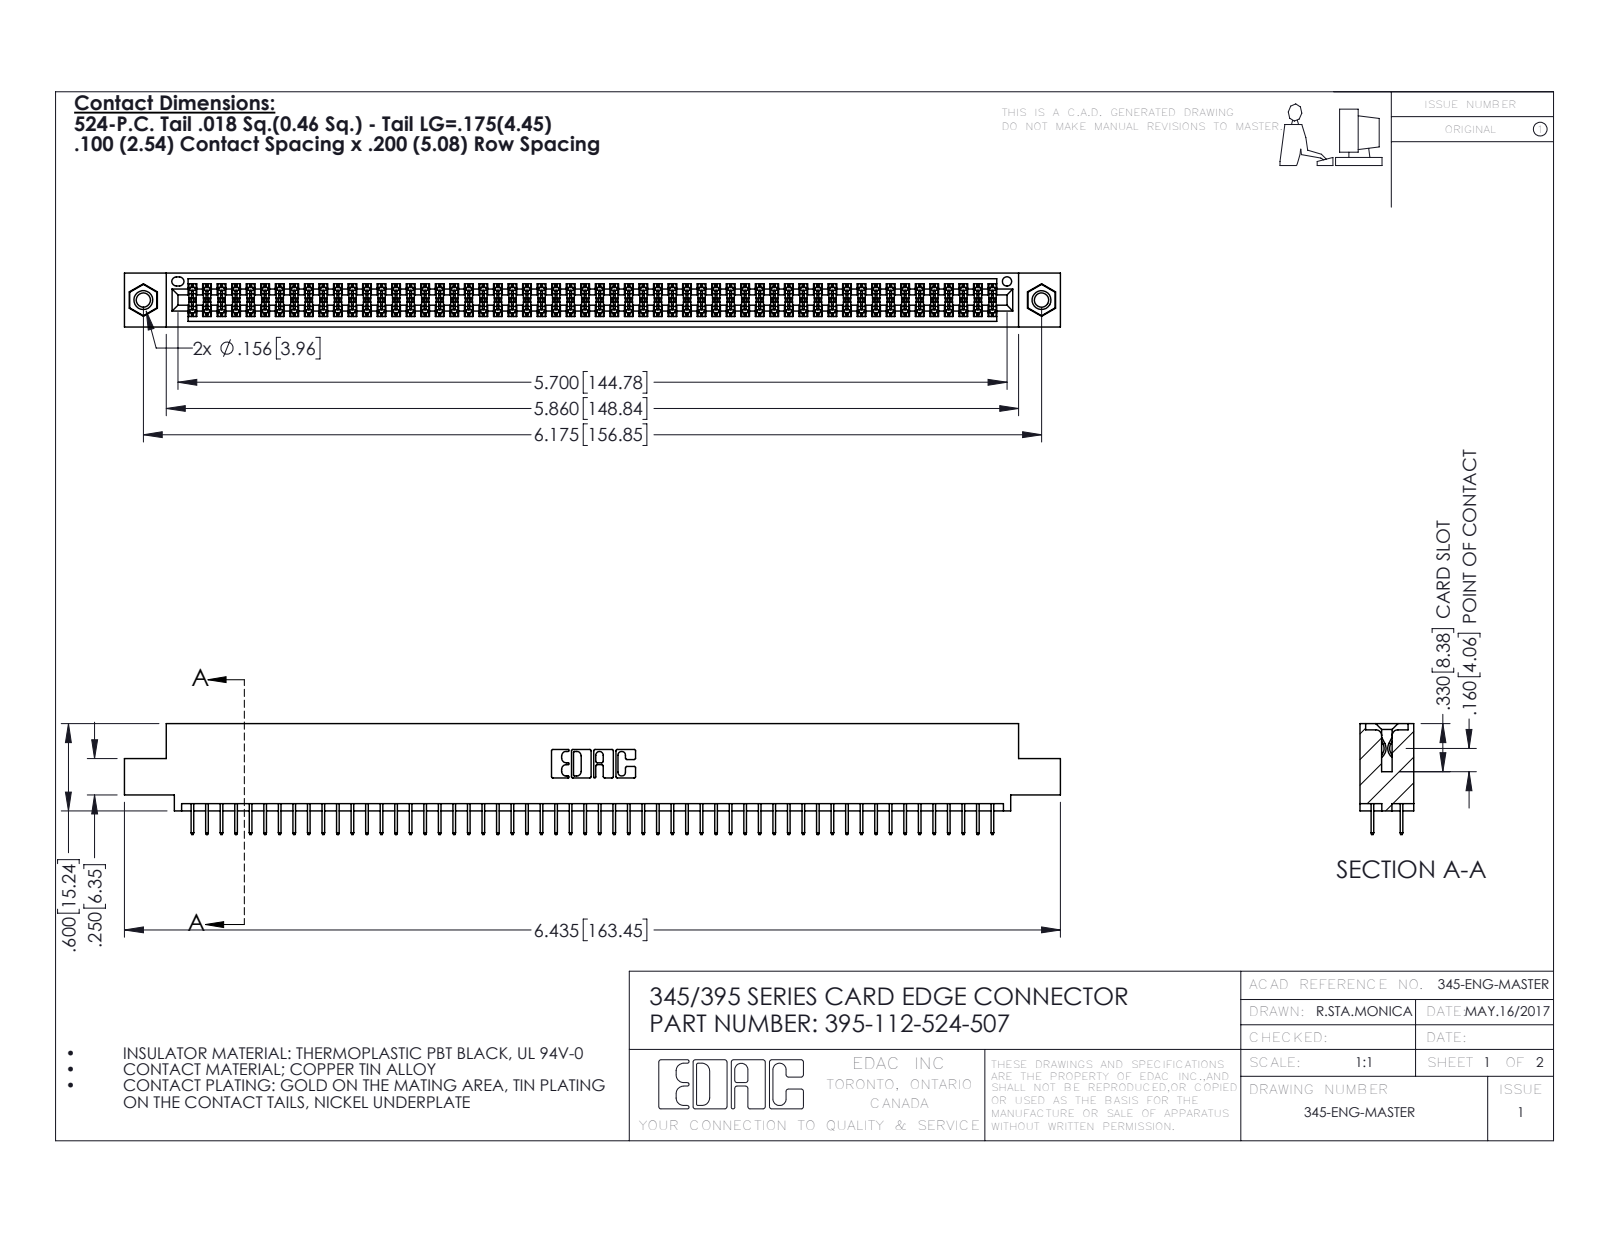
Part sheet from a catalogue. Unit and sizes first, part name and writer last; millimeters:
Units: millimetres
Overall size (bounding box): 163.4 × 19.4 × 9.4
Round holes (diameter × count): ⌀2.5 ×2, ⌀3.2 ×2, ⌀4 ×2, ⌀1.6 ×1
Round bosses / shafts (diameter × count): ⌀3.9 ×2
Partial cylindrical surfaces — rounded edges, fillets, slot ends (radius × count): R0.2 ×168, R0.3 ×22, R0.2 ×6, R0.8 ×6, R0.7 ×3, R0.4 ×2, R0.5 ×2, R0.6 ×2
Main face-to-face distances: 1.8, 7.6, 5.1, 9.4, 2.5, 6.9, 0.6, 5.7, 1.8, 4.4
Hole centre spacings: 6.9, 150.9, 156.8
Volume: 15 700 mm³ · Surface area: 23 230 mm²
Bodies: 115 solids, 6238 faces (4484 planar, 1738 cylindrical, 16 other)
Part name (STEP PRODUCT): 395-112-524-507; 345-250-001_345-250-005-103; 345 Part_0.110 Offset - 0.156 Dia-TI; 345-292-001_345-293-124
STEP written by: SolidWorks 2016 (CONFIG_CONTROL_DESIGN)
